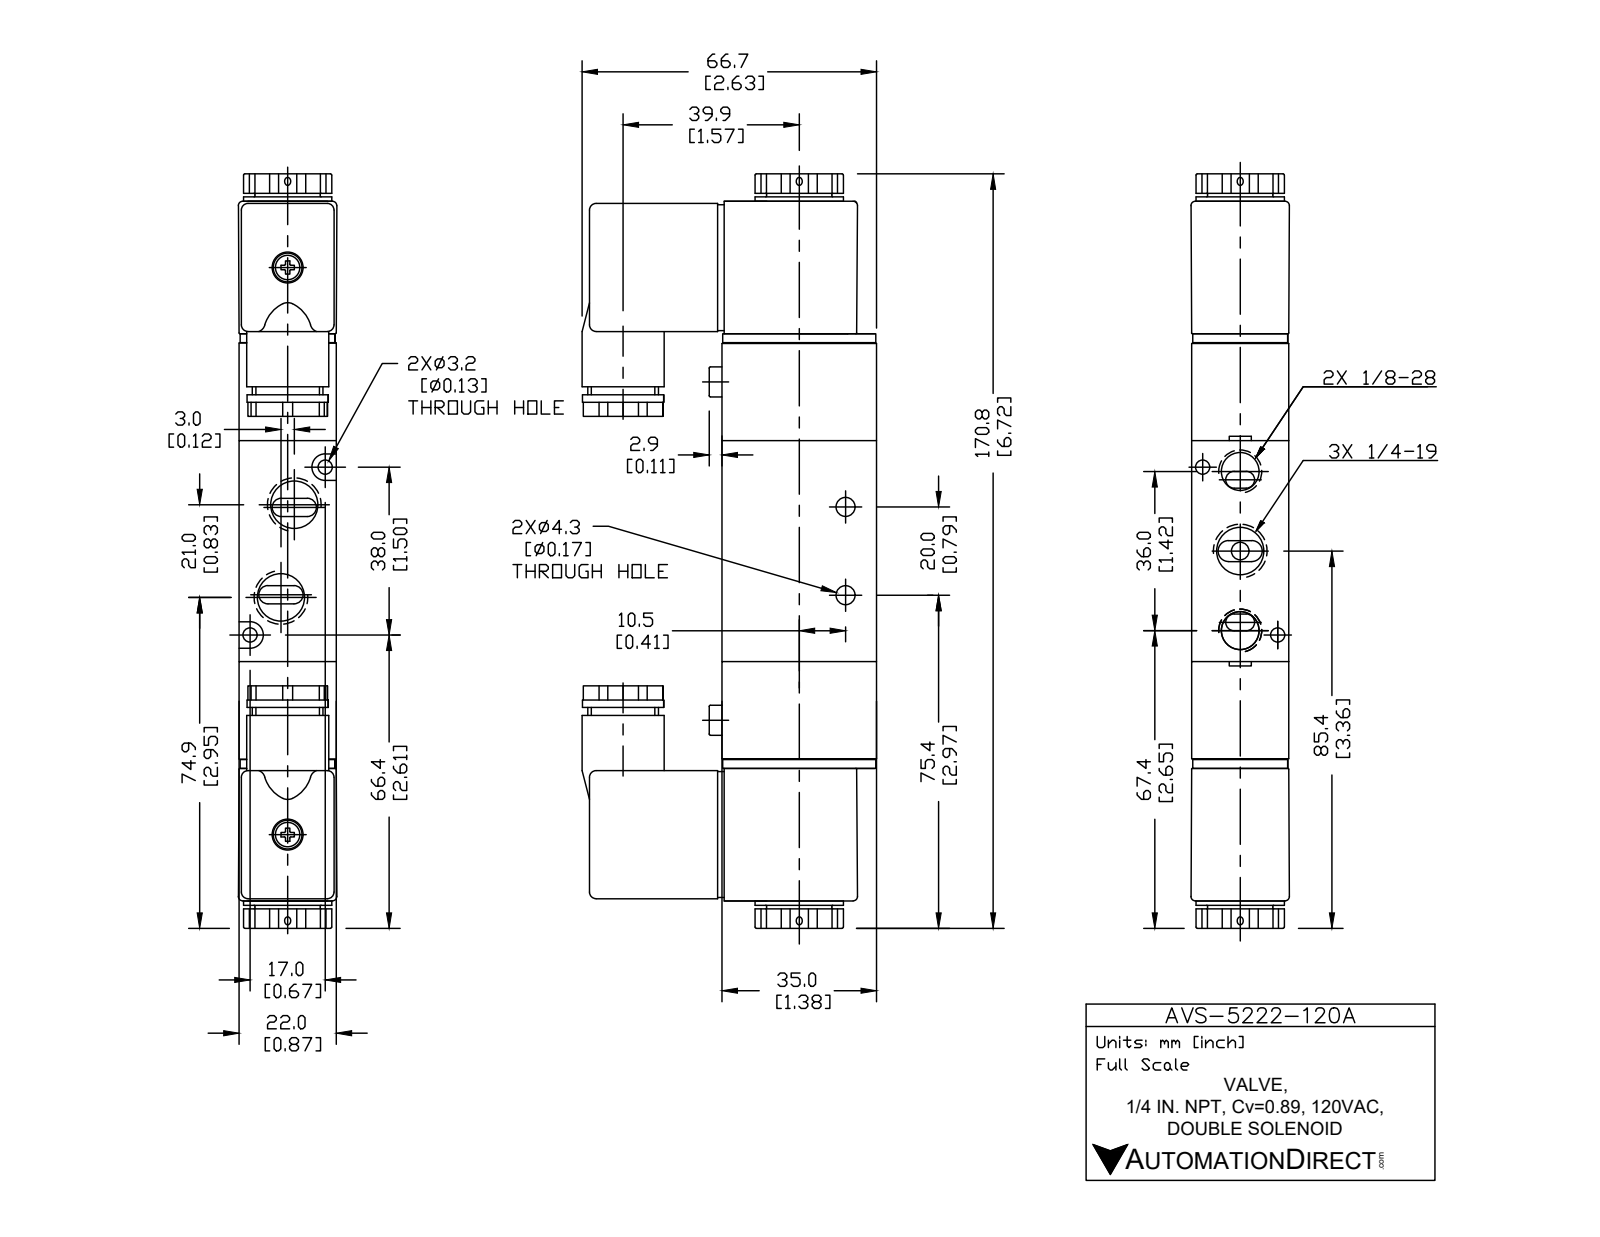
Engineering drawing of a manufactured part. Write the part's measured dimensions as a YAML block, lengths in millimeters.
part_name: "AVS-5222-120A"
step_written_by: "SolidWorks 2015 (CONFIG_CONTROL_DESIGN)"
units: millimeters
bodies: {solids: 4, faces: 272, planar: 131, cylindrical: 109, other: 32}
overall_size: [170.8, 66.7, 22]
volume: 155487
surface_area: 35796
round_holes:
  - {diameter: 11.13, count: 3}
  - {diameter: 4.3, count: 2}
  - {diameter: 8.43, count: 2}
  - {diameter: 3.2, count: 1}
  - {diameter: 3.3, count: 1}
  - {diameter: 9.3, count: 1}
round_bosses_or_shafts:
  - {diameter: 20, count: 1}
  - {diameter: 18.6, count: 1}
  - {diameter: 18.4, count: 1}
  - {diameter: 16, count: 1}
  - {diameter: 14.8, count: 1}
  - {diameter: 6.7, count: 1}
partial_cylinders:
  - {radius: 1.5, count: 18}
  - {radius: 1, count: 10}
  - {radius: 1.54, count: 10}
  - {radius: 0.5, count: 8}
  - {radius: 3, count: 2}
face_to_face_distances: [0.5, 22, 21.5, 35, 22.88, 21, 50, 30, 65, 53.7]
hole_center_spacings: [8.56, 18, 20.81, 37.96, 7.54, 7.83, 10.53, 10.55]
